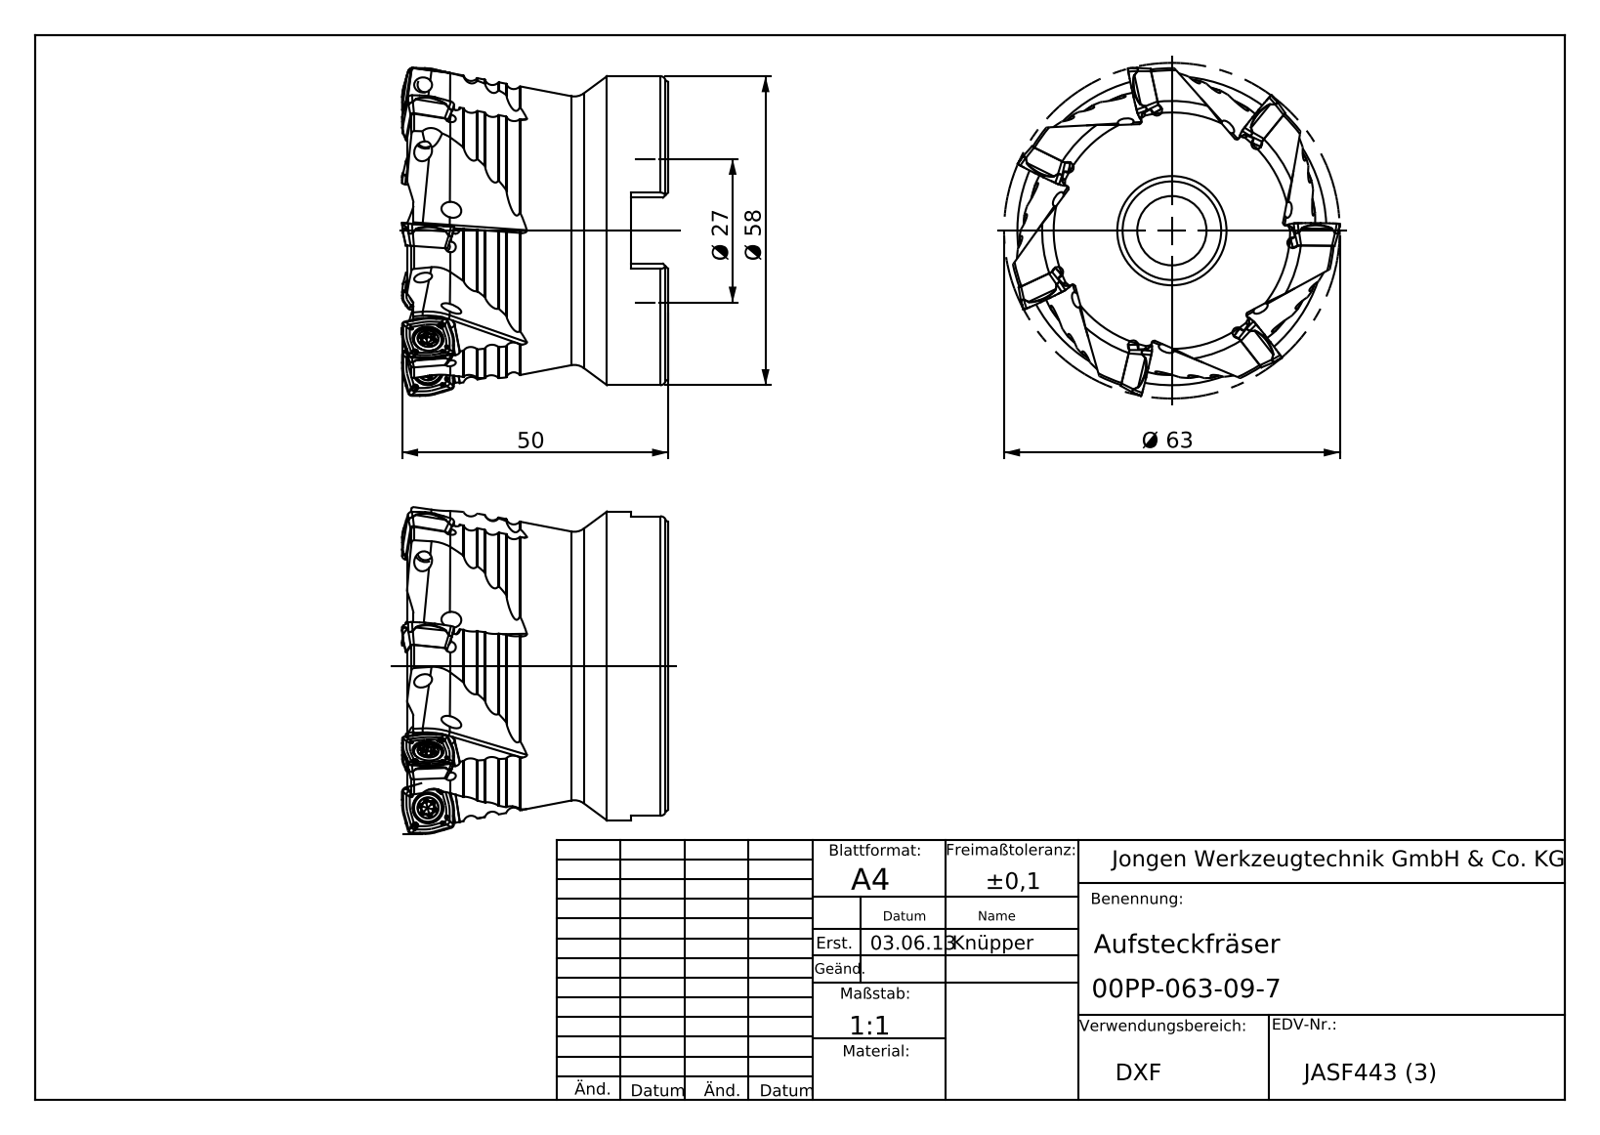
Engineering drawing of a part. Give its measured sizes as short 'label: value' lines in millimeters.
name: 00PP-063-09-7
written by: SolidWorks 2013 (AUTOMOTIVE_DESIGN)
unit: mm
bodies: 1 solid, 300 faces (96 planar, 62 cylindrical, 142 other)
size: 62.99 × 62.99 × 50.04
volume: 97 997 mm³; area: 21 021 mm²
holes: 7× ⌀3, 1× ⌀13, 1× ⌀18.5, 1× ⌀26.8, 1× ⌀27.15, 1× ⌀27.3
bosses: 1× ⌀58
rounds: 14× R0.5, 14× R0.8, 14× R1, 7× R2
face distances: 47.75, 7, 40.75, 12.4, 34, 27, 13.75, 22, 15, 12
